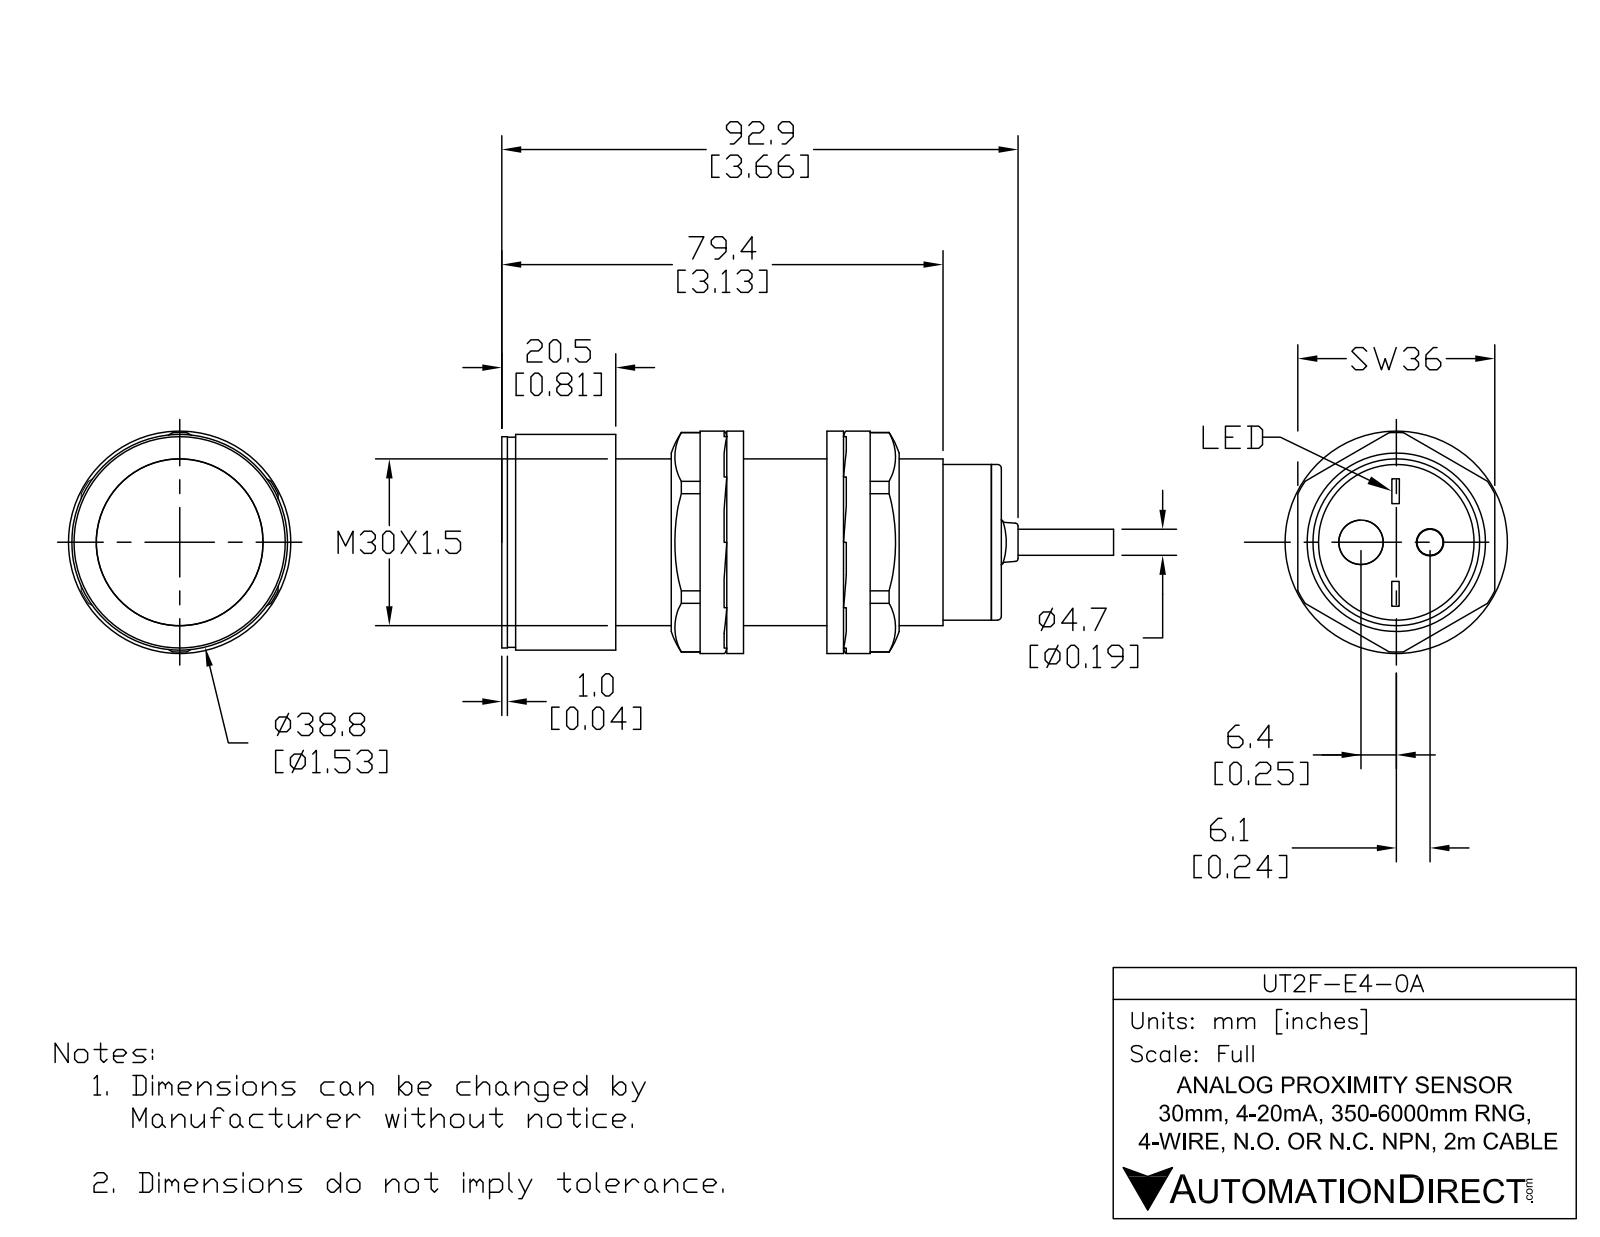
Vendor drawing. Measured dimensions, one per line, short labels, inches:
name: UT2F-E4-0A
written by: SolidWorks 2017 (AUTOMOTIVE_DESIGN)
unit: in
bodies: 5 solids, 49 faces (14 planar, 20 cylindrical, 15 other)
size: 5.043 × 1.528 × 1.528
volume: 4.38 in³; area: 24.02 in²
holes: 1× ⌀0.185, 1× ⌀0.315, 1× ⌀1.299
bosses: 1× ⌀1.528, 1× ⌀1.488, 1× ⌀1.181, 1× ⌀1.102
face distances: 3.37, 0.059, 3.429, 0.767, 0.709, 2.661, 3.5, 3.441, 2.732, 0.071
hole spacings: 0.239, 0.25, 0.49
